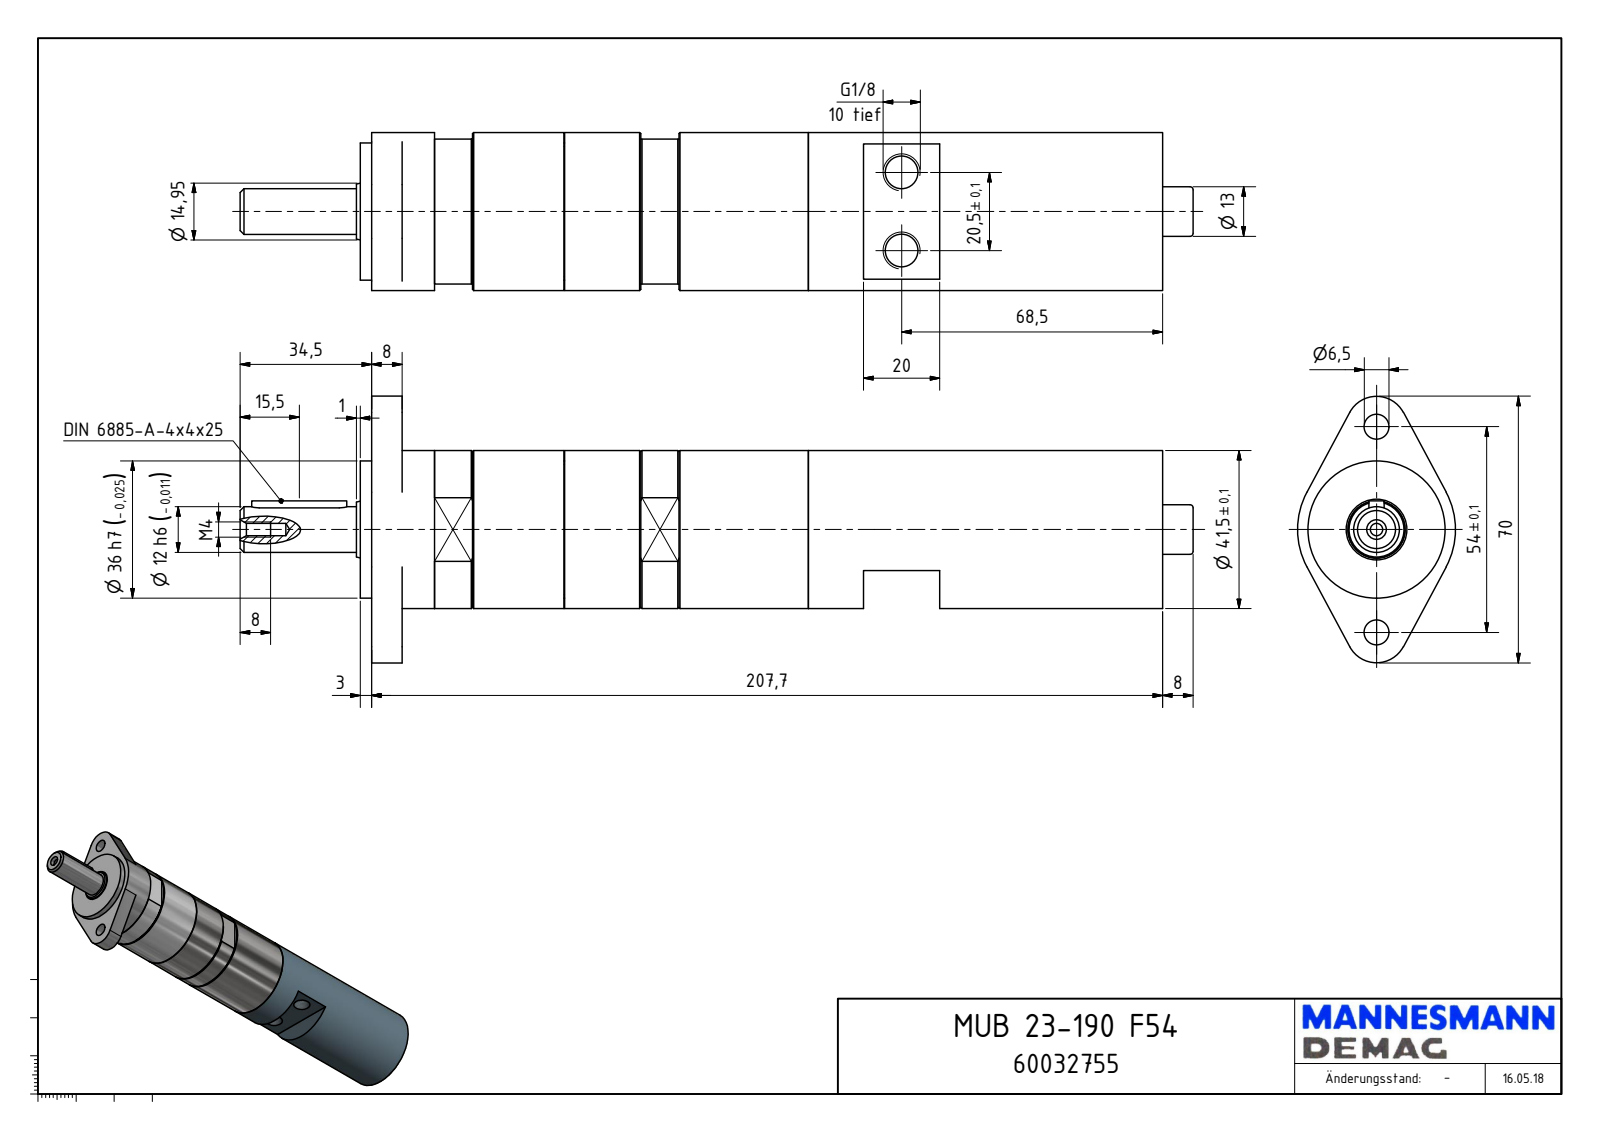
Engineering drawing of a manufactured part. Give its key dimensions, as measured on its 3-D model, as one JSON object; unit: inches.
{"part_name": "MUB 23-190 F54_60032755", "step_written_by": "Autodesk Inventor 2018 (AUTOMOTIVE_DESIGN)", "units": "inches", "bodies": {"solids": 1, "faces": 92, "planar": 44, "cylindrical": 29, "other": 19}, "overall_size": [9.85, 2.756, 1.634], "volume_in3": 17.33, "surface_area_in2": 57.39, "round_holes": [[0.256, 2], [0.337, 2], [0.128, 1], [0.63, 1], [1.555, 1]], "round_bosses_or_shafts": [[1.634, 1], [1.575, 1], [1.535, 1], [1.417, 1], [0.589, 1], [0.512, 1], [0.472, 1]], "partial_cylinders_radius": [[0.079, 2], [0.315, 2]], "face_to_face_distances": [8.177, 0.118, 8.295, 0.315, 0.433, 7.862, 1.633, 3.091, 1.496, 5.874], "hole_center_spacings": [1.063, 0.807, 2.126]}
